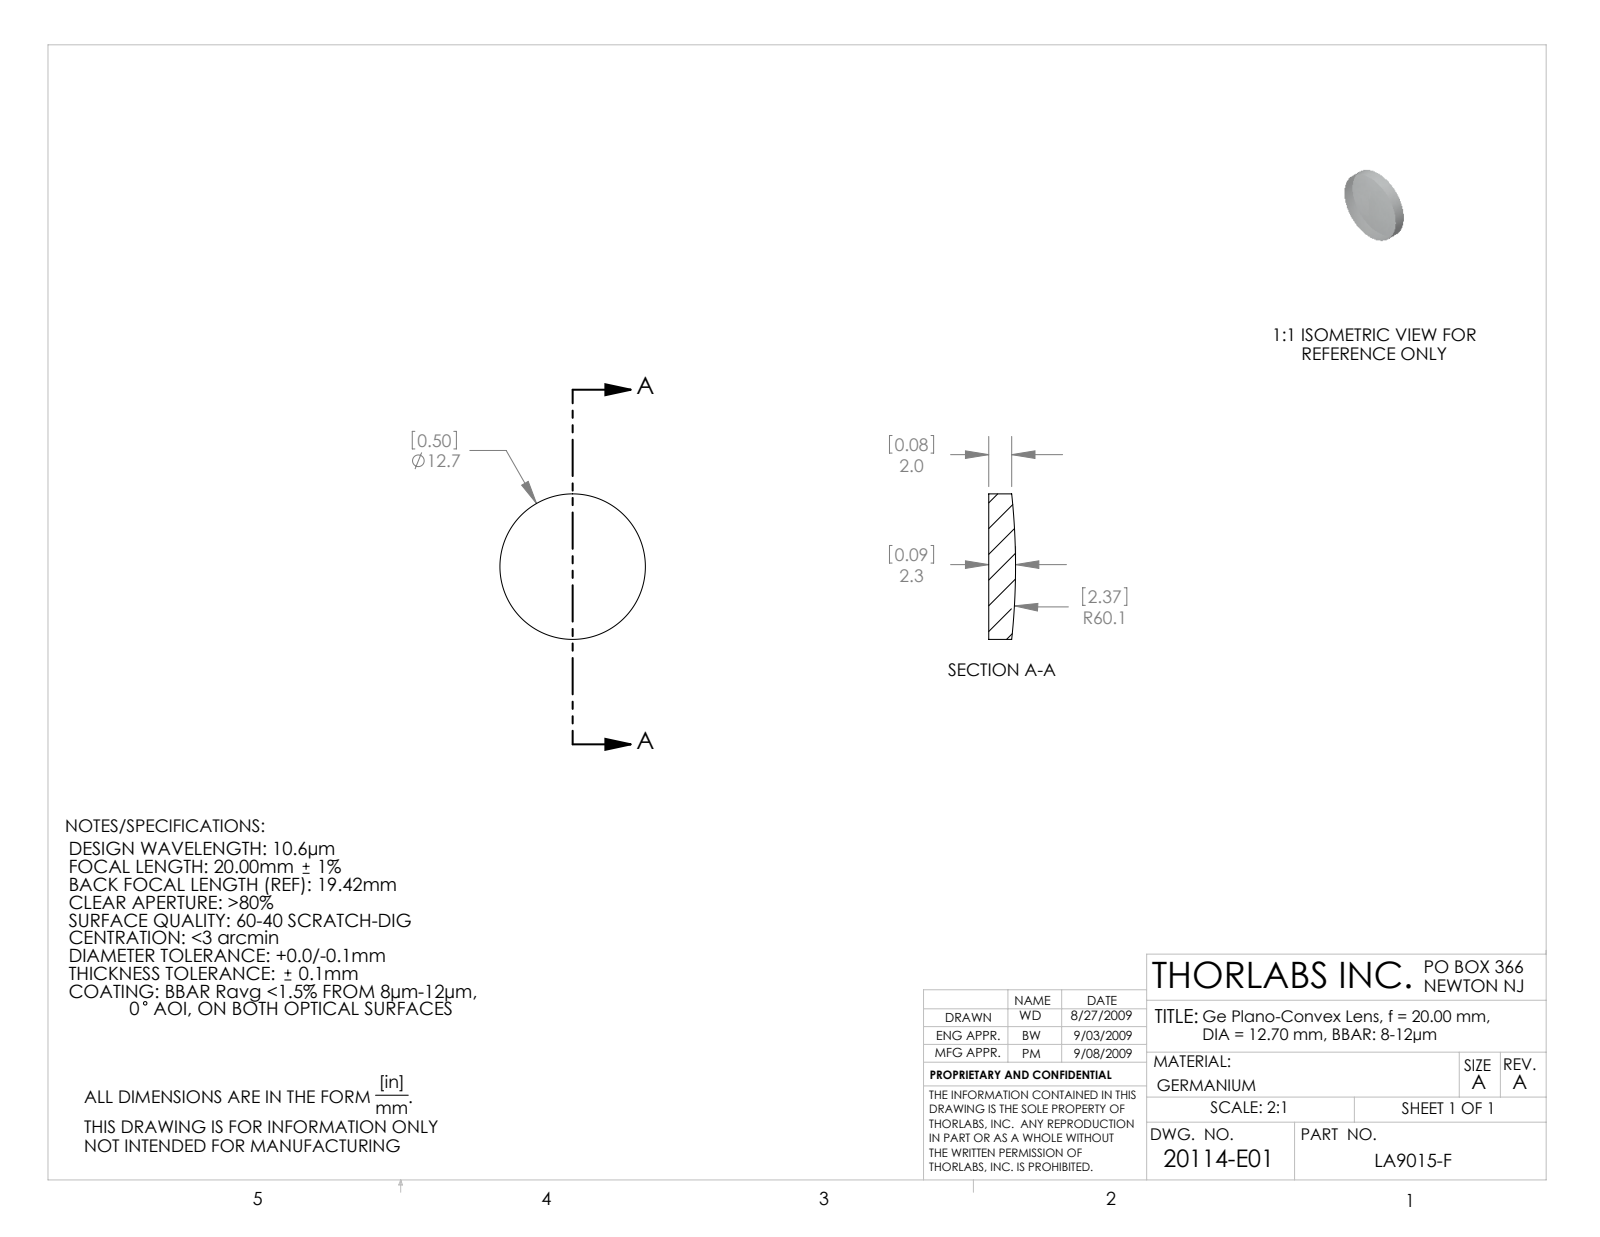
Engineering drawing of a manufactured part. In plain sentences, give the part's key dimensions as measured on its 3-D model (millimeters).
The part is named "20114-E0W". Its 3-D file was written by "SolidWorks 2007 (CONFIG_CONTROL_DESIGN)". It is 1 solid with 5 faces: 1 planar, 2 cylindrical and 2 other. Overall it measures 12.7 by 12.7 by 2.34 millimeters. Its volume is 275 cubic millimeters and its surface area 334 square millimeters. Round bosses or shafts: 1 of diameter 12.7.
